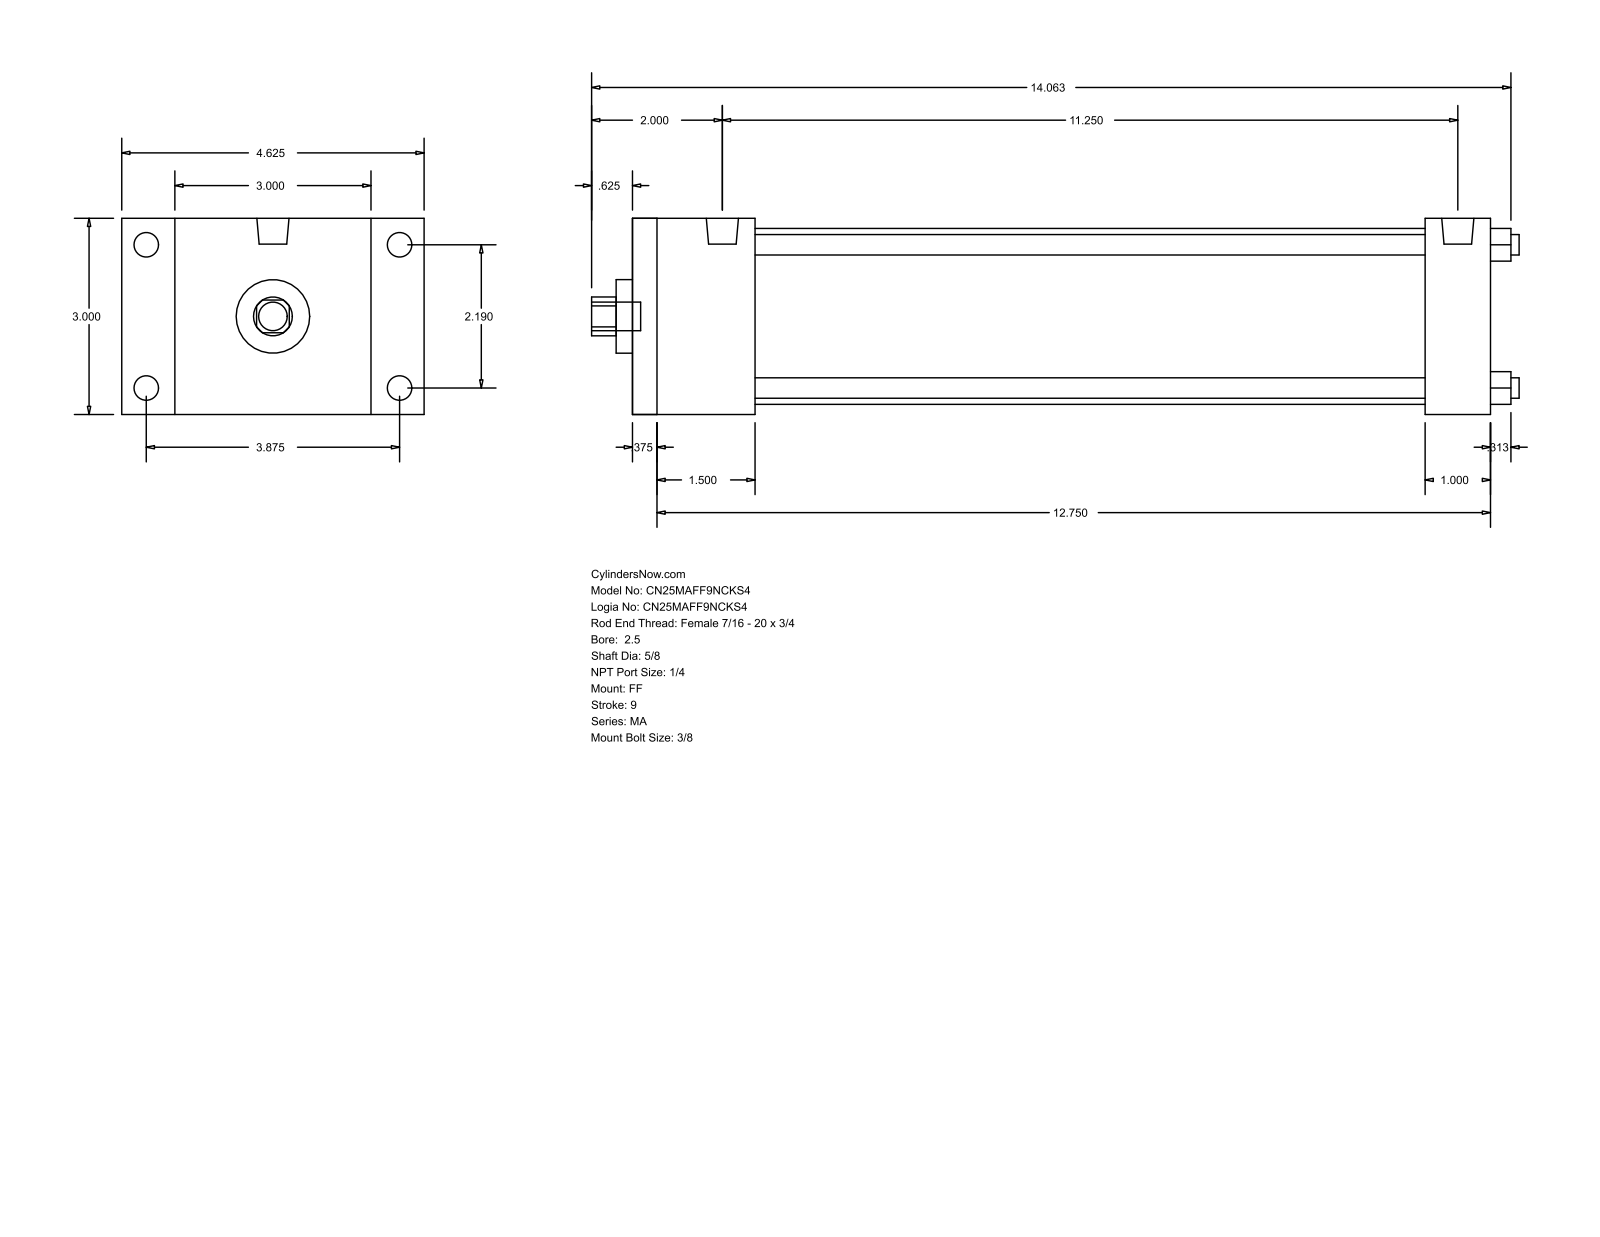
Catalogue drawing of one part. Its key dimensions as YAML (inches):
part_name: "MA_FF__0250_0.625"
step_written_by: "GSSL Pune (CONFIG_CONTROL_DESIGN)"
units: inches
bodies: {solids: 0, faces: 92, planar: 64, cylindrical: 28, other: 0}
overall_size: [14.187, 4.625, 3]
round_holes:
  - {diameter: 0.313, count: 4}
  - {diameter: 0.625, count: 1}
  - {diameter: 1.125, count: 1}
  - {diameter: 2.69, count: 1}
round_bosses_or_shafts:
  - {diameter: 0.375, count: 4}
  - {diameter: 0.313, count: 4}
  - {diameter: 0.492, count: 2}
  - {diameter: 0.437, count: 1}
partial_cylinders:
  - {radius: 0.297, count: 1}
face_to_face_distances: [3, 13.125, 0.375, 12.75, 1, 1.875, 12.125, 1.5, 11.75, 10.25]
hole_center_spacings: [1.548, 2.19, 3.097]
